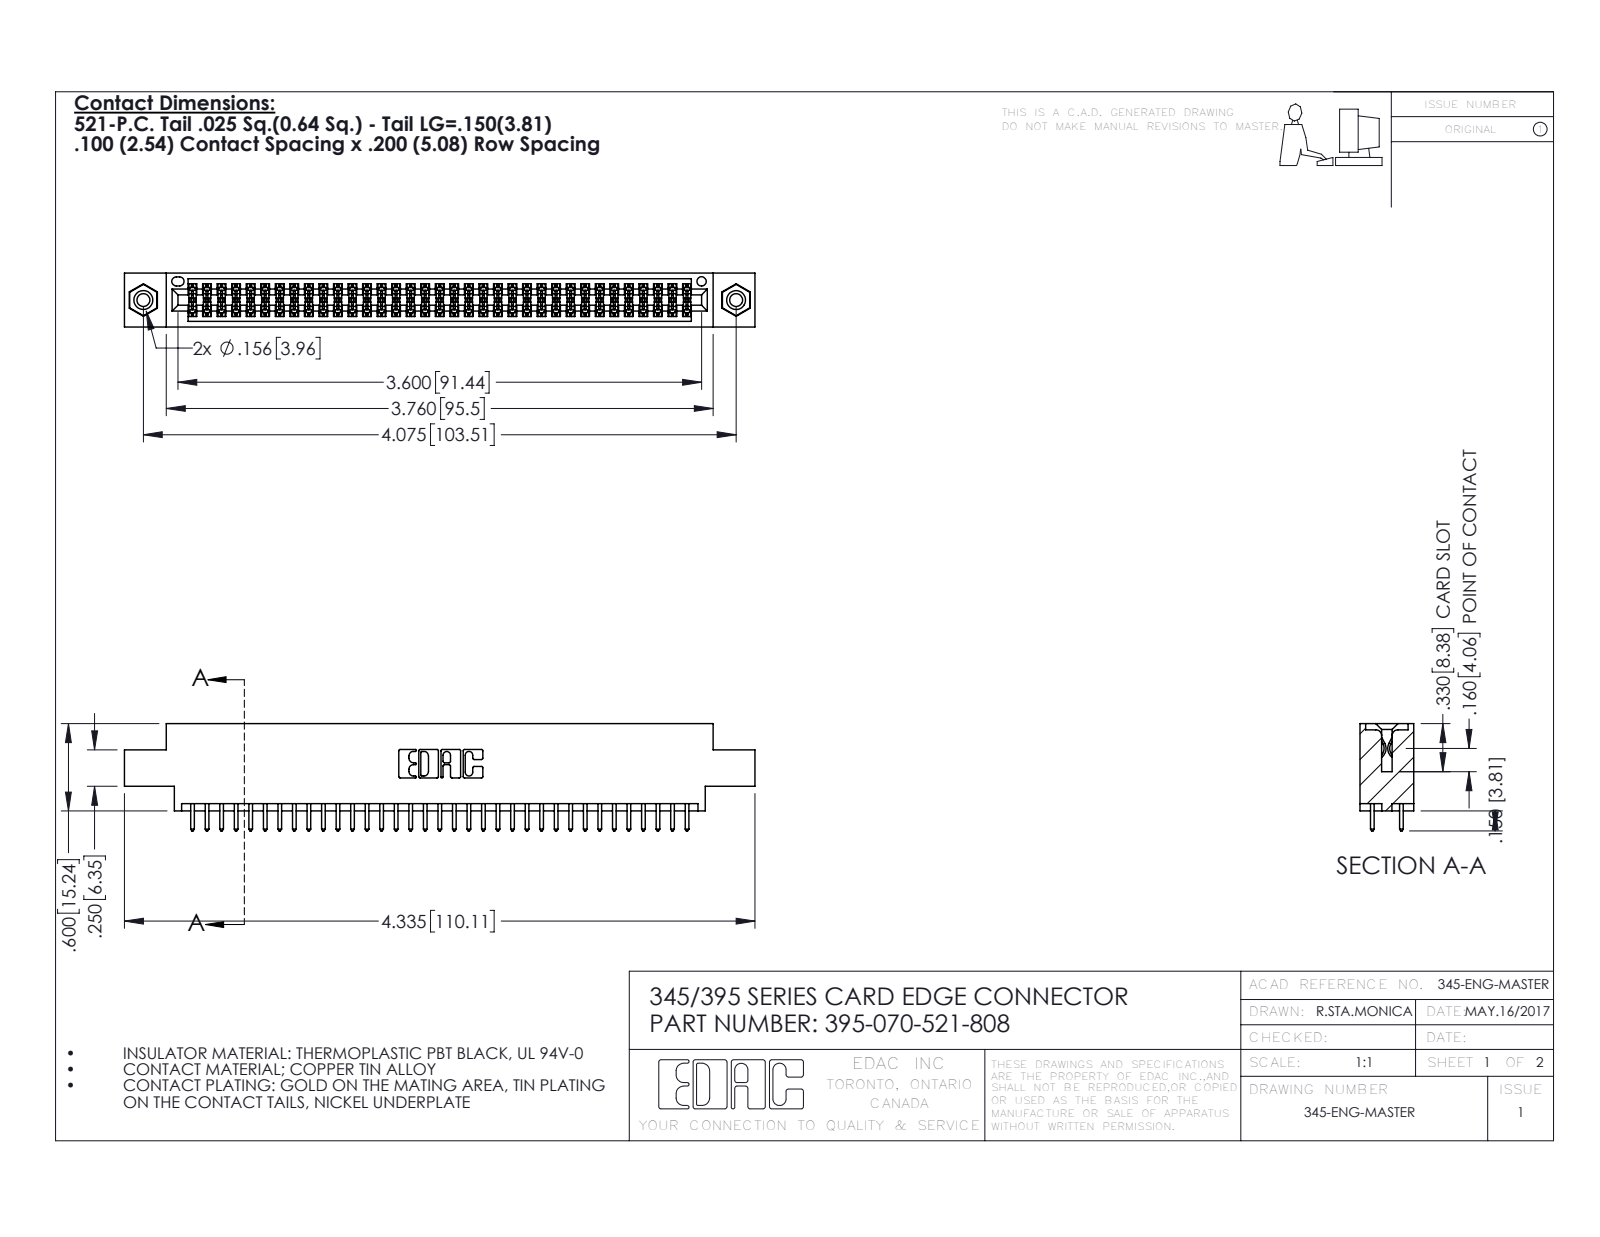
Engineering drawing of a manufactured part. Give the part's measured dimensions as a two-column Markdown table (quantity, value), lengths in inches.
| quantity | value |
| --- | --- |
| part name | 345 Part_0.170 Offset - 0.156 Dia-TI; 395-070-521-808; 345-292-001_345-293-121; 345-250-001_345-250-003-102 |
| STEP written by | SolidWorks 2016 (CONFIG_CONTROL_DESIGN) |
| units | inches |
| bodies | 73 solids, 3690 faces (2426 planar, 1248 cylindrical, 16 other) |
| overall size | 4.335 × 0.737 × 0.37 |
| volume | 0.64 in³ |
| surface area | 23.76 in² |
| round holes (diameter × count) | 0.089 × 2, 0.125 × 2, 0.156 × 2, 0.064 × 1 |
| round bosses / shafts (diameter × count) | 0.155 × 2 |
| partial cylindrical surfaces (radius × count) | 0.006 × 105, 0.01 × 70, 0.01 × 22, 0.007 × 6, 0.031 × 6, 0.026 × 3, 0.014 × 2, 0.019 × 2 |
| main face-to-face distances | 0.072, 0.298, 0.37, 0.2, 0.098, 0.272, 0.025, 0.225, 0.175, 0.149 |
| hole center spacings | 0.27, 3.839, 4.075 |
